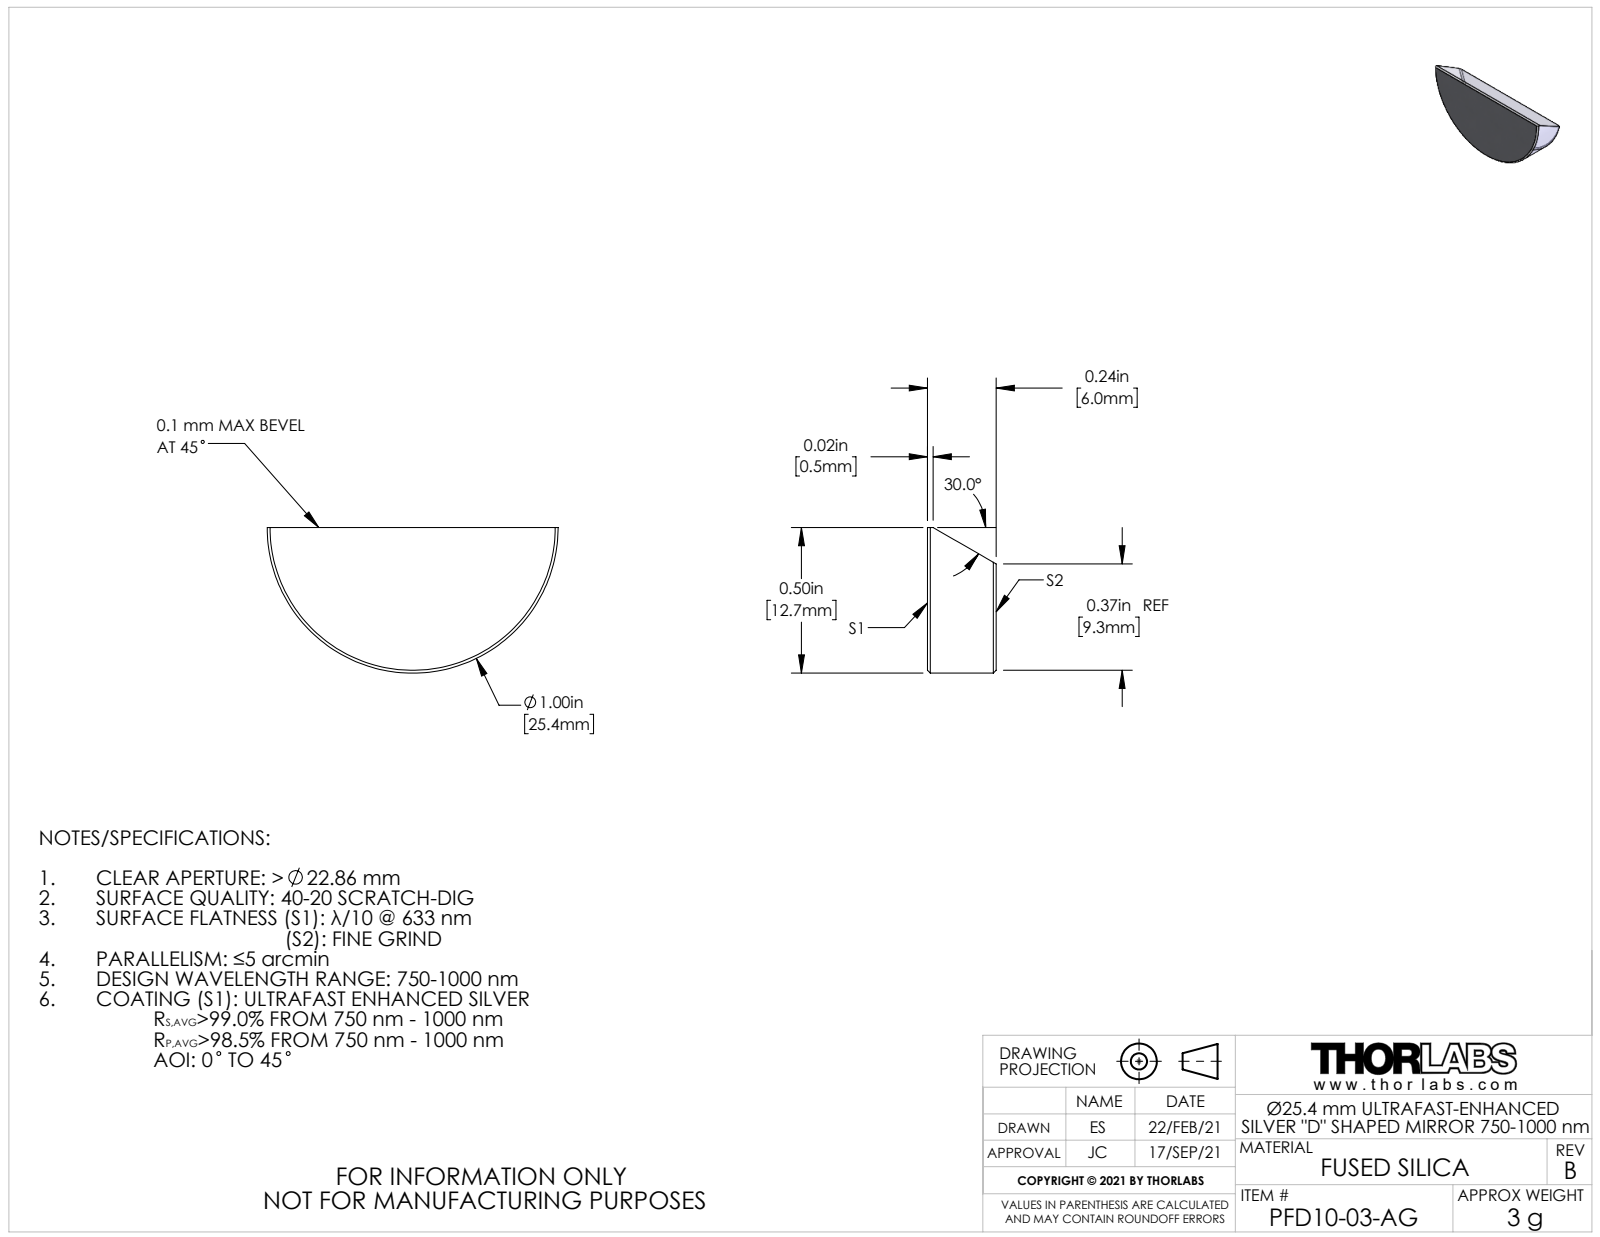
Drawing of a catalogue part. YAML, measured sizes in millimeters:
part_name: "TTN227577-E0W"
step_written_by: "SolidWorks 2018 (CONFIG_CONTROL_DESIGN)"
units: millimeters
bodies: {solids: 1, faces: 7, planar: 4, cylindrical: 1, other: 2}
overall_size: [25.4, 12.7, 6]
volume: 1297
surface_area: 810
partial_cylinders:
  - {radius: 12.7, count: 1}
face_to_face_distances: [6]
